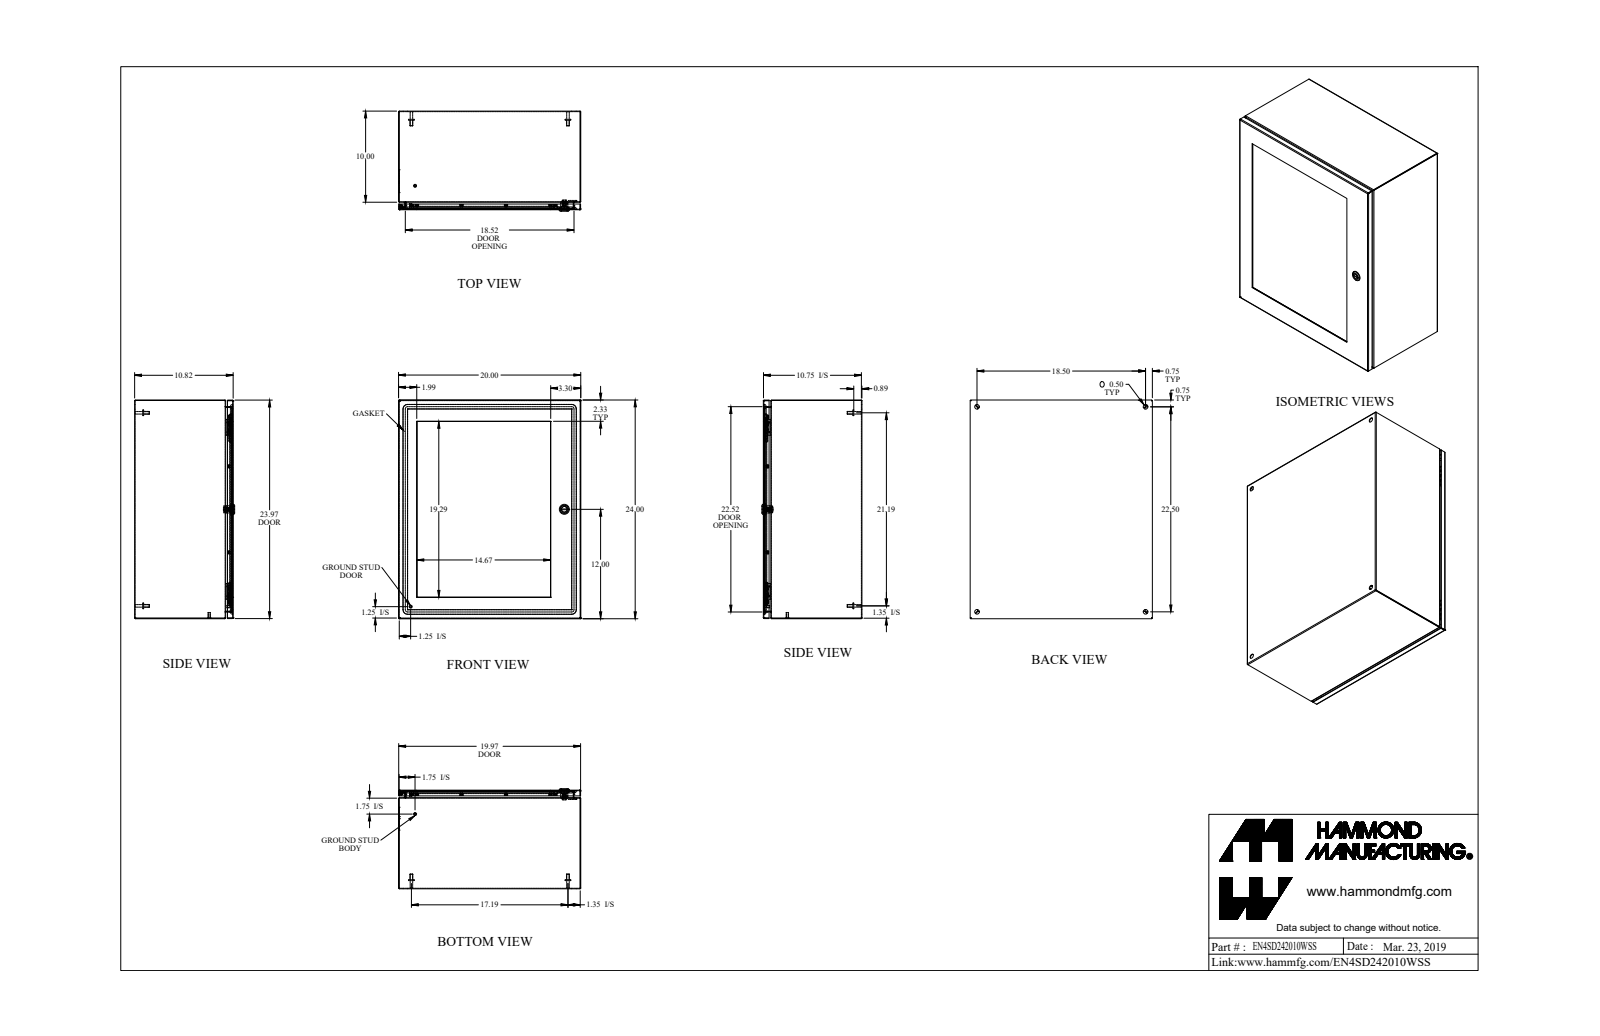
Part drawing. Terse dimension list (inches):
name: EN4SD242010WSS_Default
written by: SolidWorks 2019 (CONFIG_CONTROL_DESIGN)
unit: in
bodies: 67 solids, 1355 faces (680 planar, 407 cylindrical, 268 other)
size: 24 × 20 × 10.982
volume: 188.9 in³; area: 4 502 in²
holes: 18× ⌀0.13, 18× ⌀0.25, 5× ⌀0.5, 1× ⌀0.172, 1× ⌀0.197, 1× ⌀0.24, 1× ⌀0.242, 1× ⌀0.387, 1× ⌀0.63, 1× ⌀0.768
bosses: 19× ⌀0.226, 18× ⌀0.368, 18× ⌀0.164, 6× ⌀0.313, 4× ⌀0.625, 4× ⌀0.275, 2× ⌀0.25, 1× ⌀1.1
rounds: 21× R0.029, 21× R0.086, 12× R0.188, 10× R0.125, 4× R0.006, 4× R0.016, 4× R0.062, 4× R0.088
face distances: 0.057, 10.765, 10.708, 19.943, 23.943, 0.25, 10.458, 10.515, 19.886, 20
hole spacings: 4.719, 4.89, 4.891, 9.78, 10.324, 16.401, 18.324, 20.333
